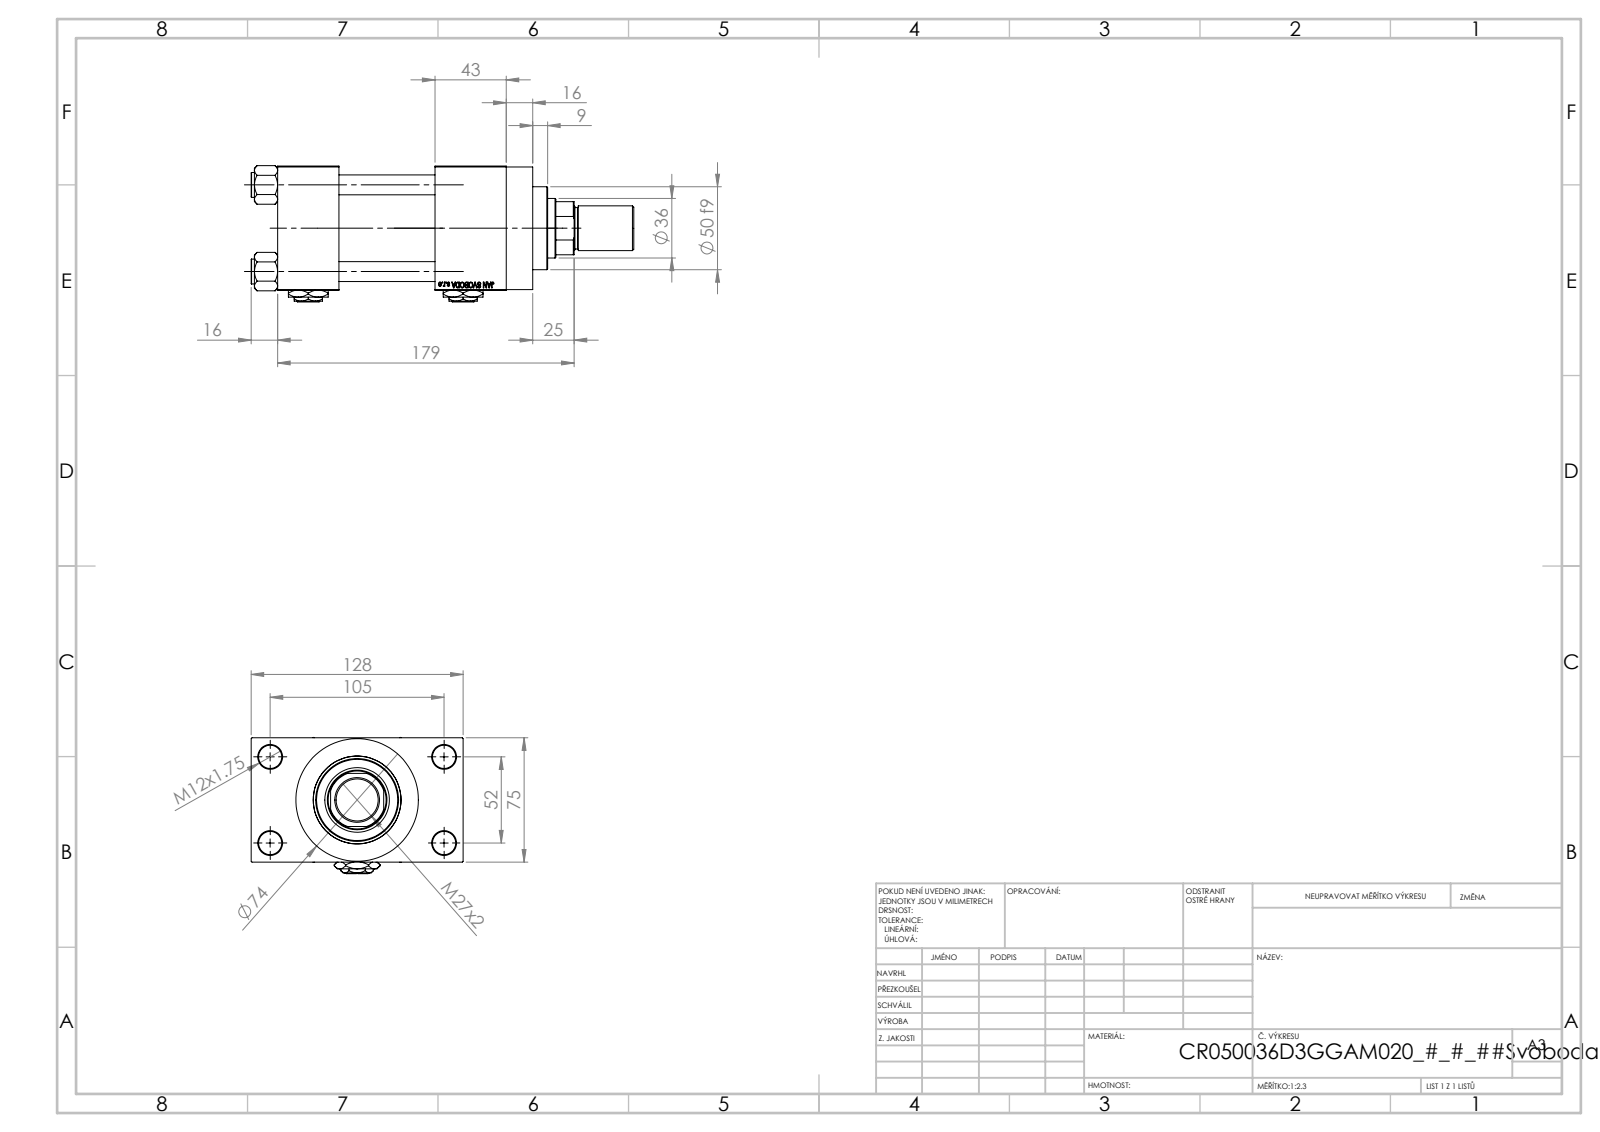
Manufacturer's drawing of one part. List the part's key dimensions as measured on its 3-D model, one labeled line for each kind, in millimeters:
Part name (STEP PRODUCT): V215CR_D_TYCINKA; V215_VC_A; V215CR_D_Body; V215CR_VCP_D (+3 more)
STEP written by: SolidWorks 2019 (CONFIG_CONTROL_DESIGN)
Units: millimetres
Bodies: 14 solids, 1219 faces (549 planar, 104 cylindrical, 566 other)
Overall size (bounding box): 231 × 128 × 82.27
Volume: 842 388 mm³ · Surface area: 182 295 mm²
Round holes (diameter × count): ⌀12 ×4, ⌀14 ×4, ⌀7 ×2, ⌀20.96 ×2, ⌀30 ×2, ⌀25.5 ×1, ⌀36 ×1, ⌀39 ×1, ⌀41 ×1, ⌀53 ×1
Round bosses / shafts (diameter × count): ⌀15 ×4, ⌀74 ×1, ⌀56 ×1, ⌀50 ×1, ⌀27 ×1, ⌀25 ×1
Partial cylindrical surfaces — rounded edges, fillets, slot ends (radius × count): R17.5 ×1
Main face-to-face distances: 75, 58, 37, 95, 101.5, 26.5, 138, 43, 101, 16
Hole centre spacings: 26.35, 36.98, 52.3, 58.43, 58.59, 78.65, 94.37, 52
